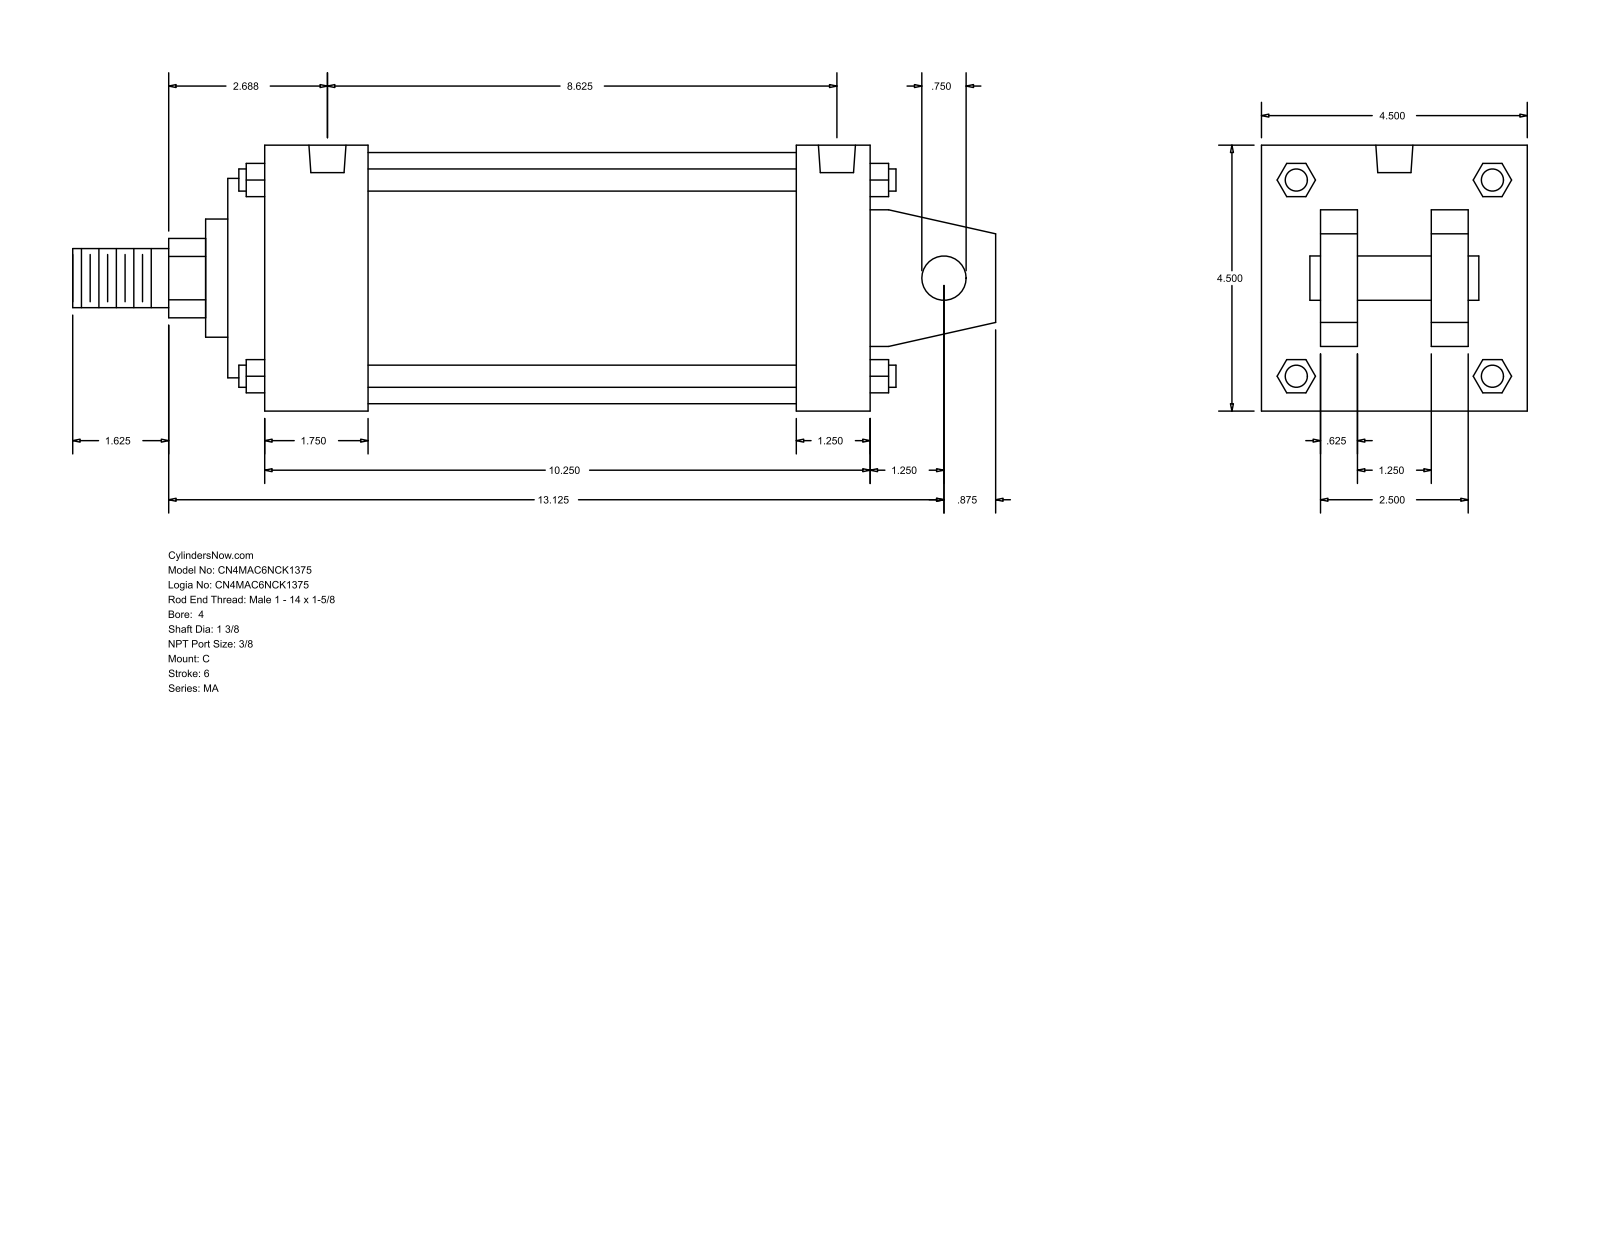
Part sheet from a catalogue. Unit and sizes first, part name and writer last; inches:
Units: inches
Overall size (bounding box): 15.625 × 4.5 × 4.5
Round holes (diameter × count): ⌀0.437 ×4, ⌀0.627 ×2
Round bosses / shafts (diameter × count): ⌀0.375 ×4, ⌀4.25 ×1, ⌀3.375 ×1, ⌀2 ×1, ⌀1.375 ×1, ⌀1 ×1, ⌀0.75 ×1
Partial cylindrical surfaces — rounded edges, fillets, slot ends (radius × count): R0.672 ×1
Main face-to-face distances: 4.5, 0.625, 10.25, 2.875, 1.625, 1, 3.5, 1.875, 10.875, 9.625
Hole centre spacings: 0.188, 8.25, 8.437, 8.625
Bodies: 0 solids, 141 faces (109 planar, 32 cylindrical, 0 other)
Part name (STEP PRODUCT): MA_C__0400_1.375
STEP written by: GSSL Pune (CONFIG_CONTROL_DESIGN)
